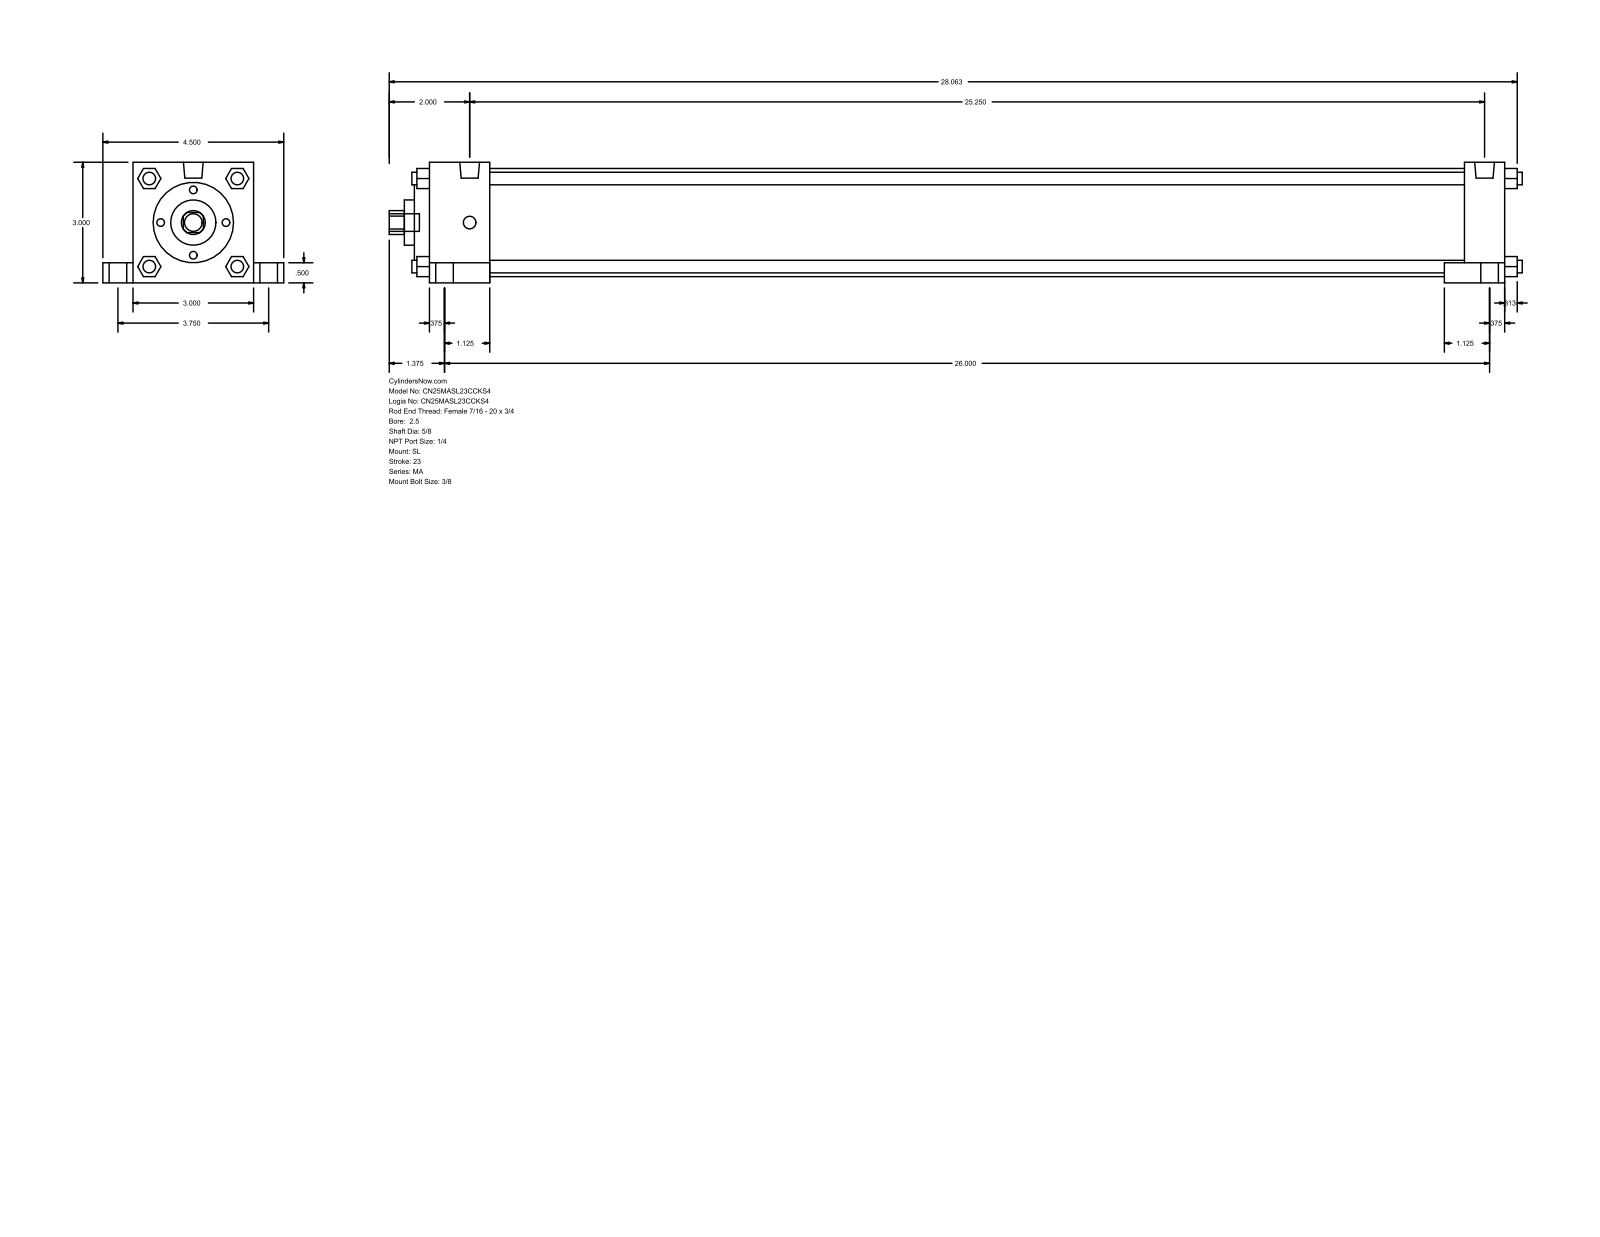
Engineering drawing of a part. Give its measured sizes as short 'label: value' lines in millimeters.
name: MA_SL__0250_0.625
written by: GSSL Pune (CONFIG_CONTROL_DESIGN)
unit: mm
bodies: 0 solids, 150 faces (113 planar, 37 cylindrical, 0 other)
size: 715.96 × 114.3 × 76.2
holes: 1× ⌀15.88, 1× ⌀28.57, 1× ⌀50.8, 1× ⌀68.33
bosses: 8× ⌀7.94, 5× ⌀11.11, 4× ⌀17.46, 2× ⌀12.49
rounds: 1× R7.54
face distances: 76.2, 679.45, 12.7, 615.95, 25.4, 38.1, 641.35, 654.05, 19.05, 63.5
